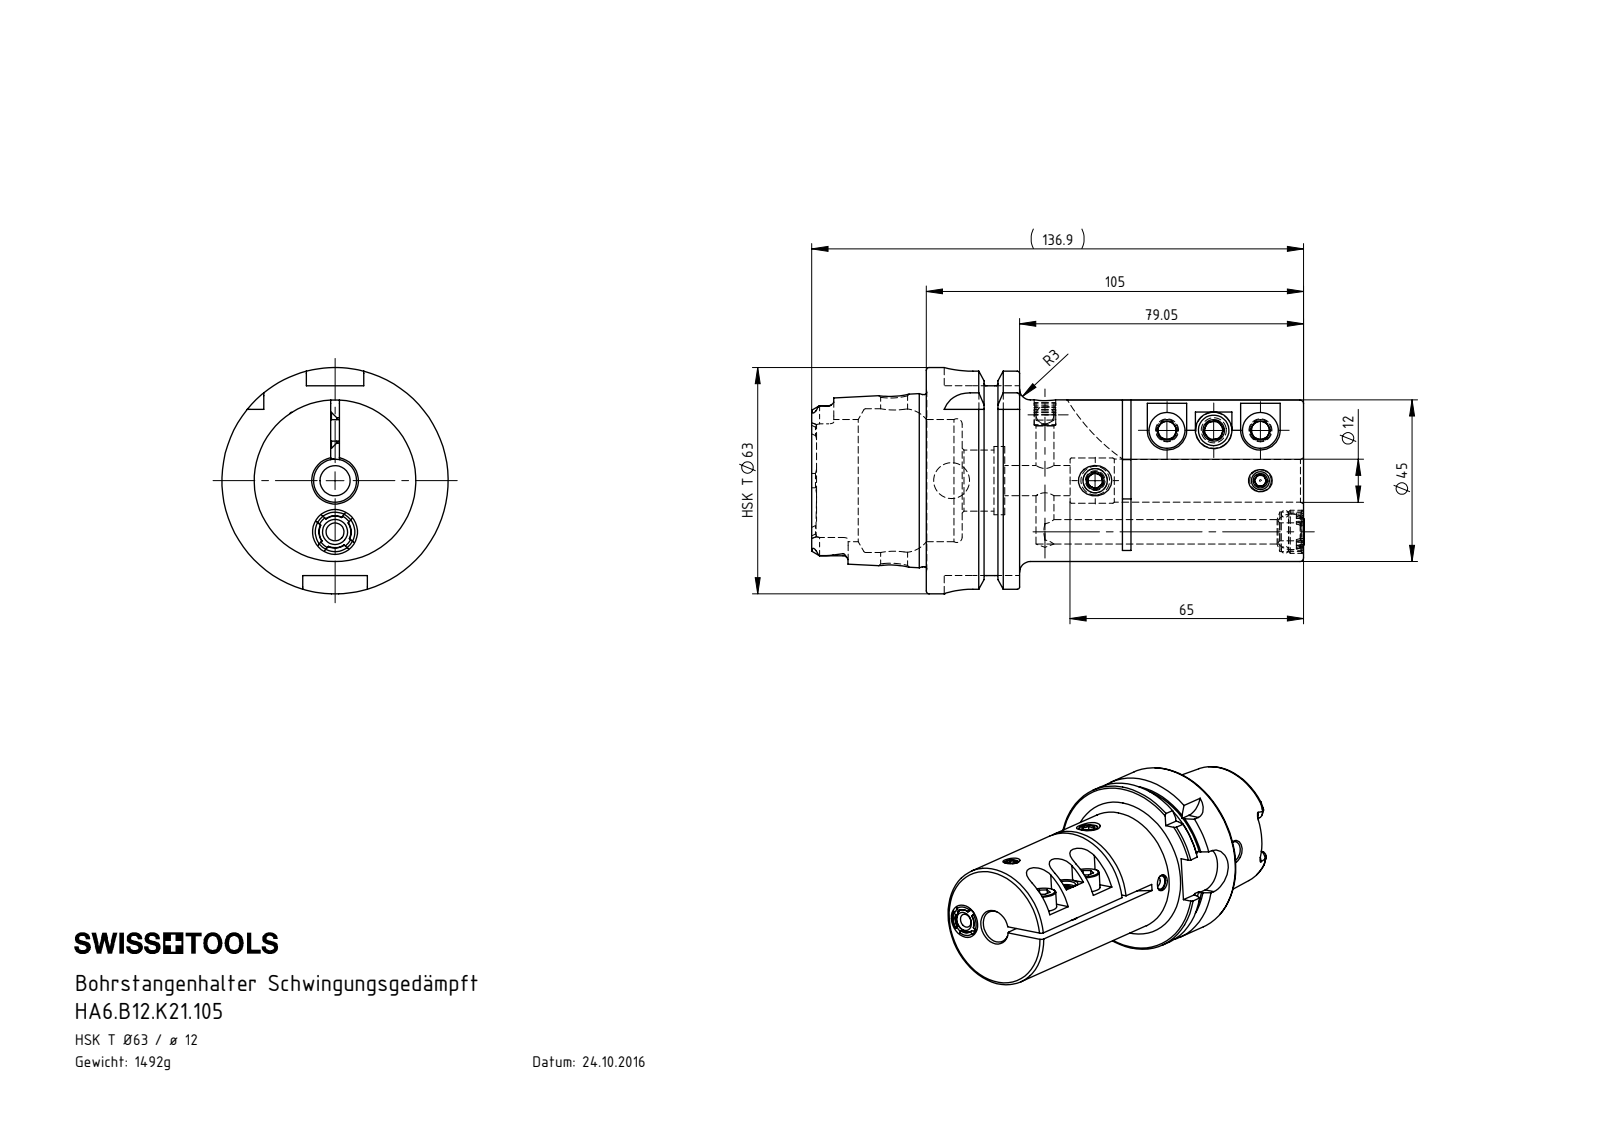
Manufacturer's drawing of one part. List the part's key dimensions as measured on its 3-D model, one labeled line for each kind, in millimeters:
Part name (STEP PRODUCT): DIN 3771 - 8x1.5; HA6.B12.K21.105; ISO 4028 - M8 x 16; KU1-U12.002.010_A (+7 more)
STEP written by: SolidWorks 2017 (AUTOMOTIVE_DESIGN)
Units: millimetres
Bodies: 11 solids, 344 faces (154 planar, 74 cylindrical, 116 other)
Overall size (bounding box): 137.85 × 63 × 63
Volume: 189 799 mm³ · Surface area: 46 671 mm²
Round holes (diameter × count): ⌀5 ×5, ⌀6.4 ×2, ⌀6.8 ×2, ⌀10 ×2, ⌀4 ×1, ⌀7.5 ×1, ⌀8.4 ×1, ⌀8.5 ×1, ⌀11 ×1, ⌀12 ×1, ⌀12.6 ×1, ⌀17 ×1
Round bosses / shafts (diameter × count): ⌀6 ×4, ⌀10 ×3, ⌀63 ×1, ⌀54.95 ×1, ⌀47.94 ×1, ⌀45 ×1, ⌀12 ×1, ⌀8 ×1
Partial cylindrical surfaces — rounded edges, fillets, slot ends (radius × count): R1.4 ×6, R2.88 ×4, R8 ×4, R6 ×2, R4.4 ×1, R5.1 ×1, R52 ×1, R55 ×1
Main face-to-face distances: 2.4, 105, 25.95, 79.05, 16, 54.6, 28.65, 50.4, 57, 31.05
Hole centre spacings: 13, 14, 14.25, 19.1, 24.41, 26, 29.53, 35.85
